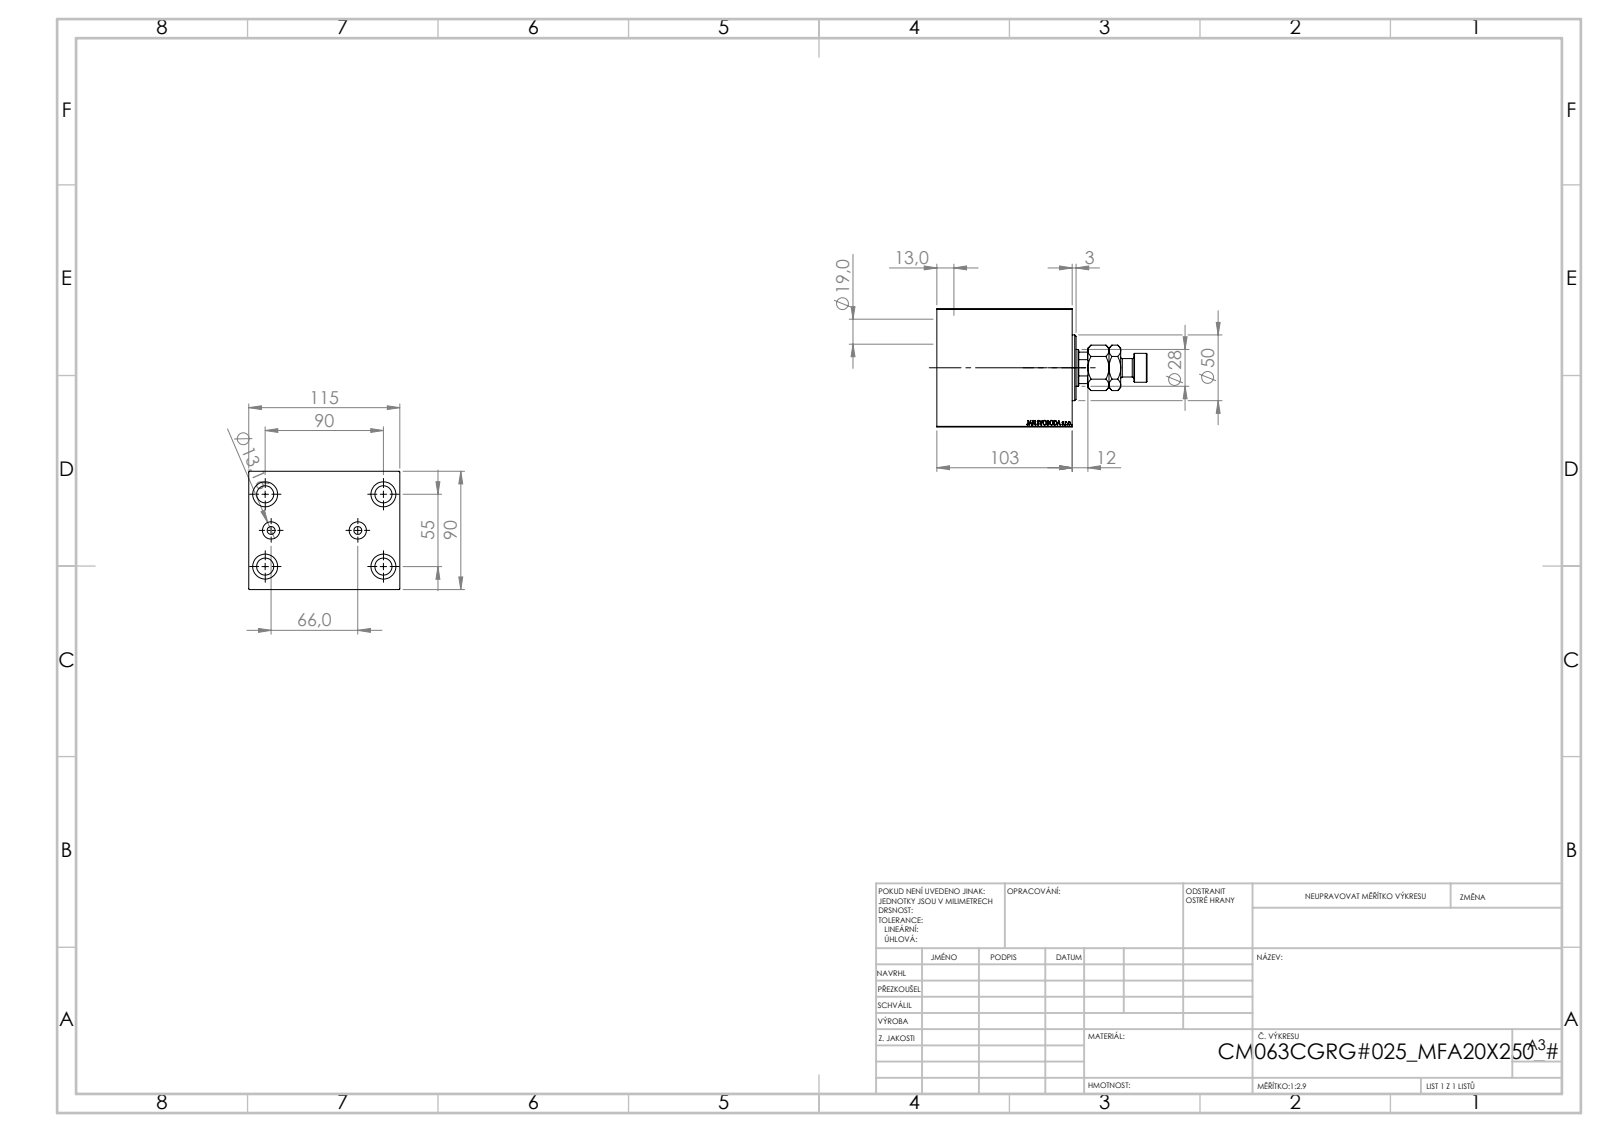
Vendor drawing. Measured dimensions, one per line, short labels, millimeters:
name: V450CM_VC_B; V450CM_C_VCP; MFA; V450CM_C_Body
written by: SolidWorks 2019 (CONFIG_CONTROL_DESIGN)
unit: mm
bodies: 4 solids, 913 faces (425 planar, 62 cylindrical, 426 other)
size: 161.5 × 115 × 90
volume: 954 612 mm³; area: 125 918 mm²
holes: 4× ⌀13, 4× ⌀19, 2× ⌀6, 2× ⌀13.16, 1× ⌀18.5, 1× ⌀28, 1× ⌀31.5, 1× ⌀63, 1× ⌀65, 1× ⌀72
bosses: 1× ⌀50, 1× ⌀22, 1× ⌀14
rounds: 1× R13.5
face distances: 90, 115, 103, 53.25, 49.75, 93, 10, 25, 5, 43.25
hole spacings: 30, 52.74, 82.71, 33, 55, 90, 105.48, 66
